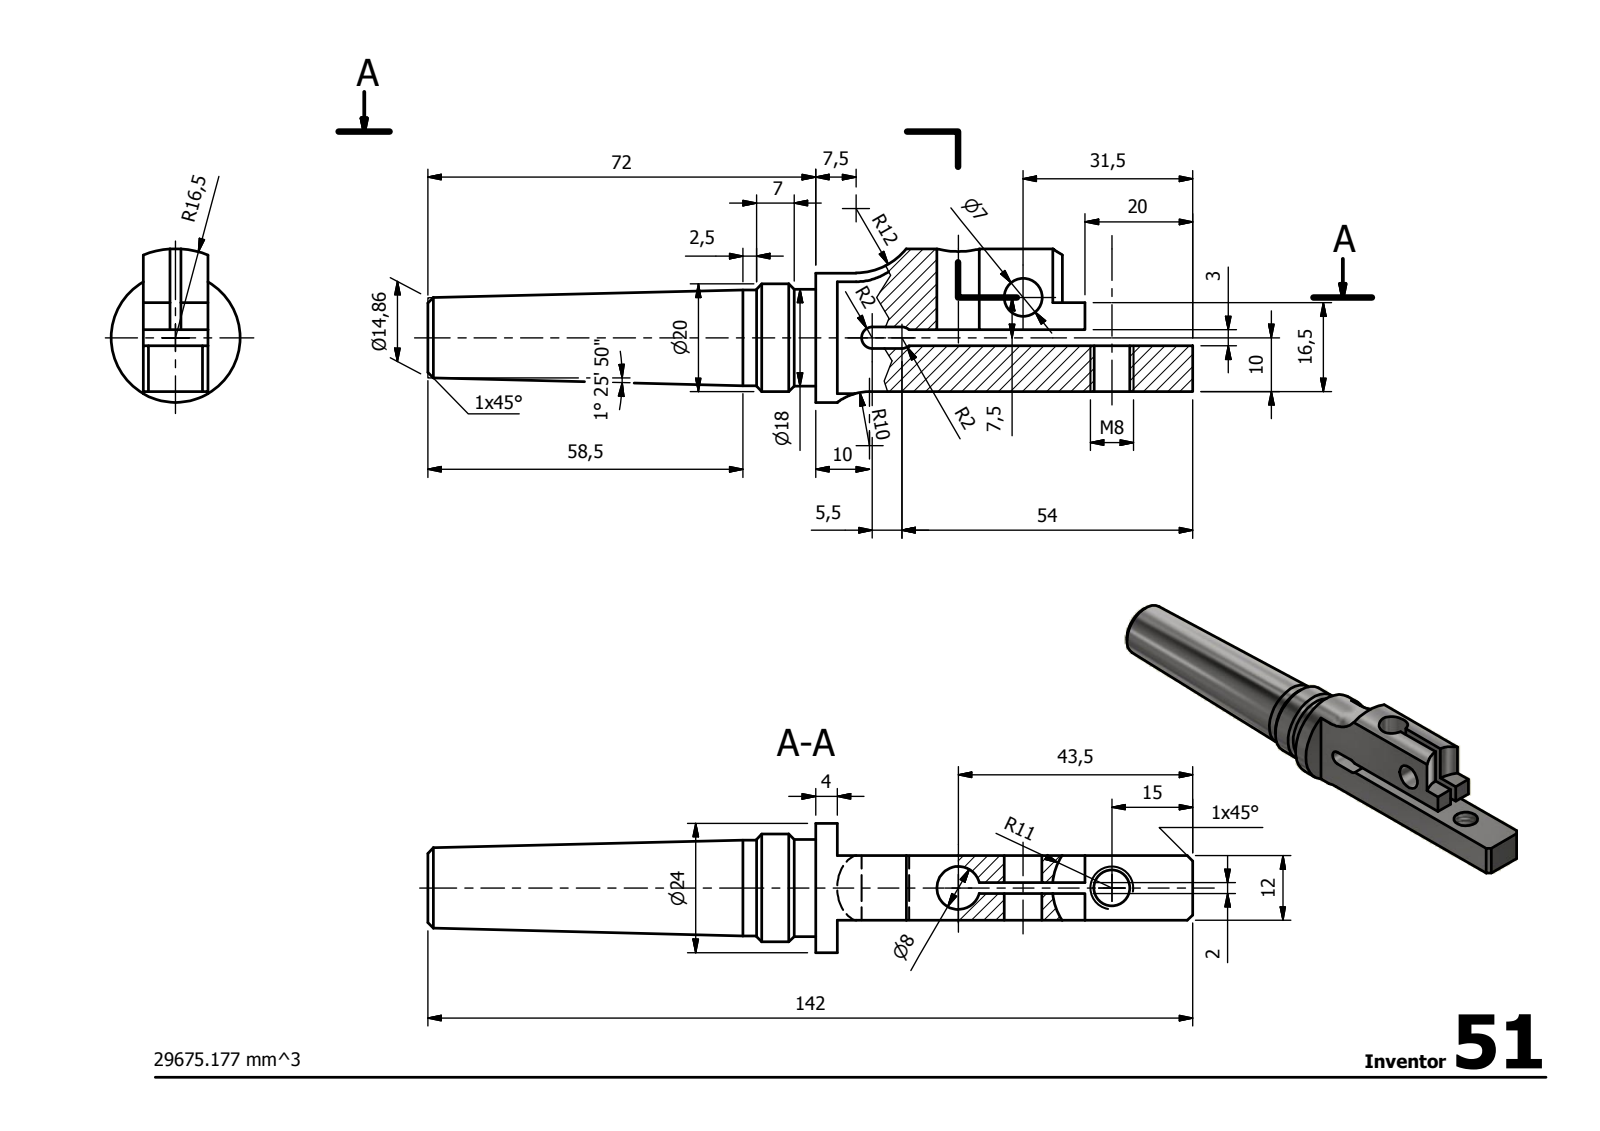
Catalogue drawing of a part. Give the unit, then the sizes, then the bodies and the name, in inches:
Units: inches
Overall size (bounding box): 5.591 × 1.122 × 0.945
Round holes (diameter × count): ⌀0.262 ×1, ⌀0.276 ×1, ⌀0.315 ×1
Round bosses / shafts (diameter × count): ⌀0.945 ×1, ⌀0.787 ×1, ⌀0.709 ×1, ⌀0.7 ×1
Partial cylindrical surfaces — rounded edges, fillets, slot ends (radius × count): R0.079 ×2, R0.394 ×1, R0.433 ×1, R0.65 ×1
Main face-to-face distances: 0.472, 0.335, 0.197, 0.276, 0.453, 0.118, 0.157, 0.079, 0.02, 0.138
Hole centre spacings: 1.122
Volume: 1.811 in³ · Surface area: 16.45 in²
Bodies: 1 solid, 41 faces (21 planar, 15 cylindrical, 5 other)
STEP written by: Autodesk Inventor 2014 (AUTOMOTIVE_DESIGN)
